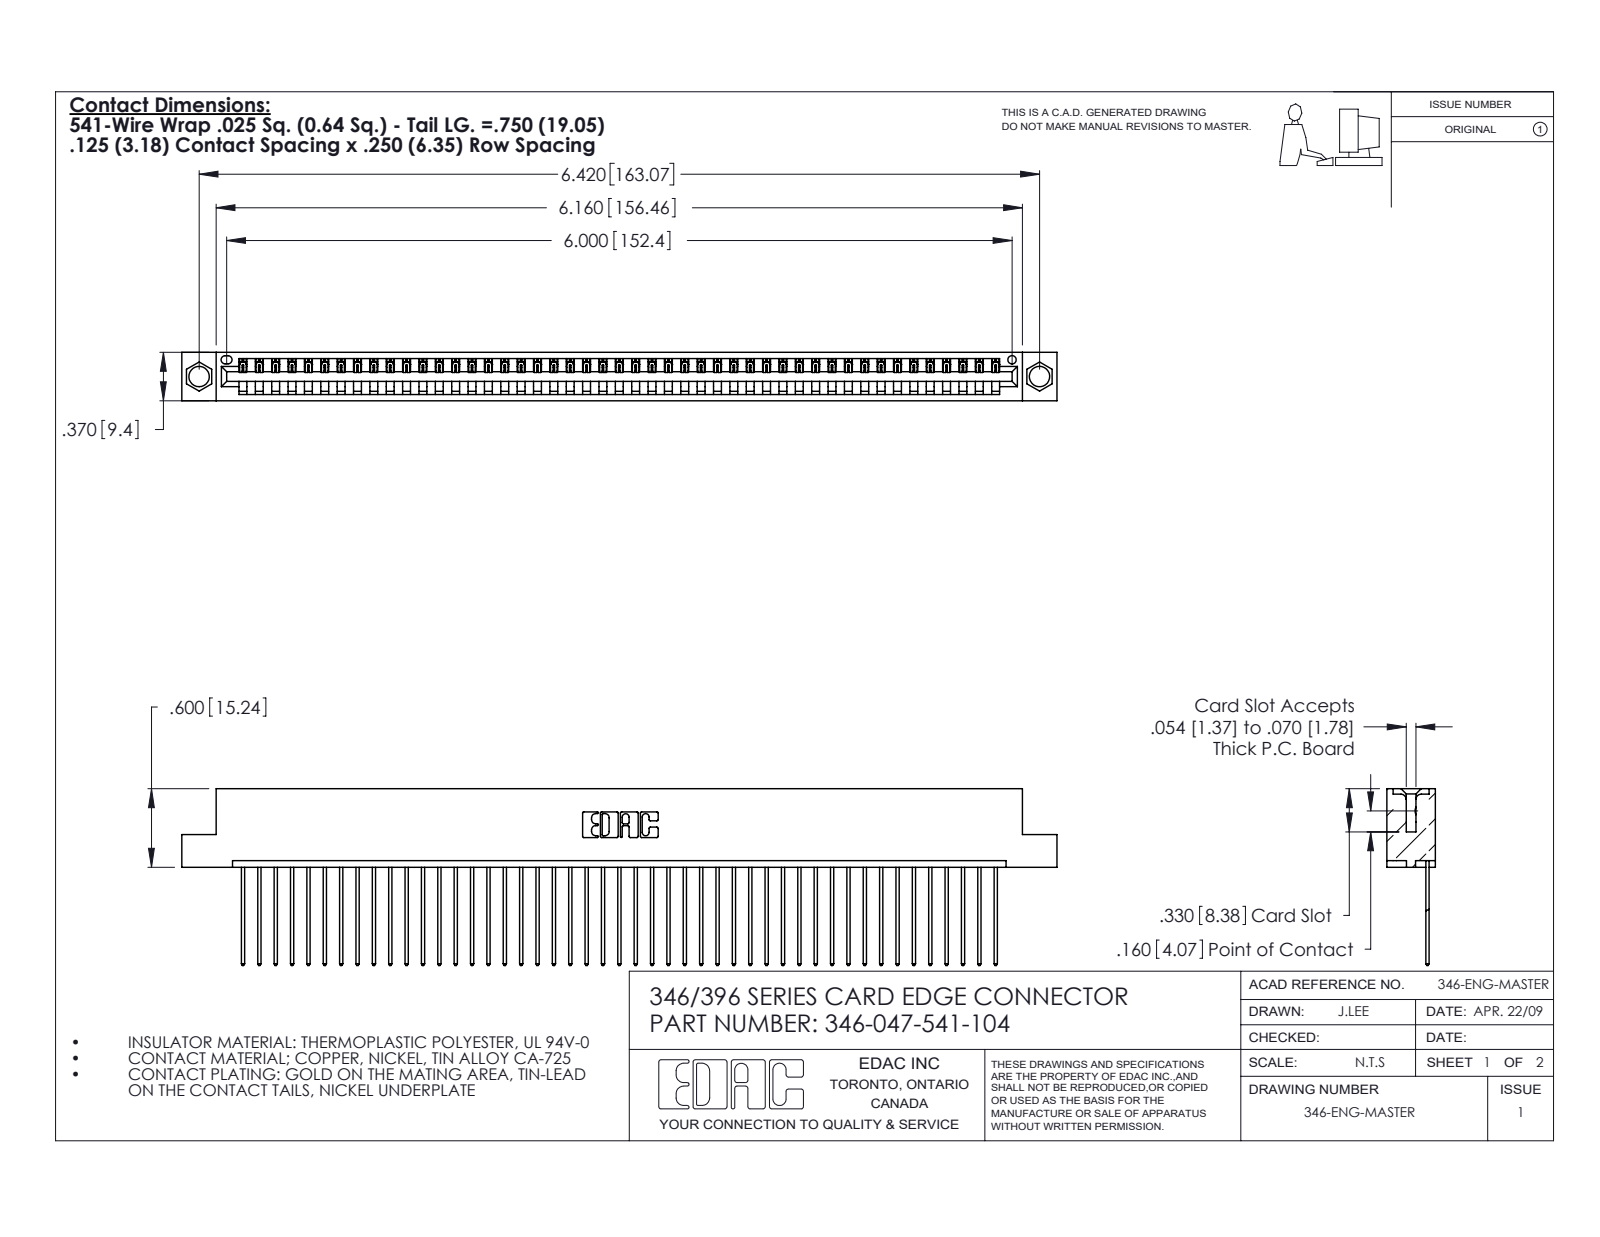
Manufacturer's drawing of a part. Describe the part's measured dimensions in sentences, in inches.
The part is named "346-047-541-104; 346 Part_Flush Mounting Lugs - 0.156 Dia-TH; 345-292-001_345-293-141". Its 3-D file was written by "SolidWorks 2020 (CONFIG_CONTROL_DESIGN)". It is 48 solids with 2862 faces: 1970 planar, 892 cylindrical and 0 other. Overall it measures 6.685 by 1.35 by 0.37 inches. Its volume is 0.997 cubic inches and its surface area 32.92 square inches. Round holes: 2 of diameter 0.156, 1 of diameter 0.064. Partial cylindrical surfaces (rounded edges, fillets, slot ends): 94 of radius 0.006, 94 of radius 0.01, 22 of radius 0.01, 6 of radius 0.007, 6 of radius 0.031, 3 of radius 0.026, 2 of radius 0.031, 2 of radius 0.04. The main face-to-face distances are 0.048, 0.322, 0.37, 0.25, 0.072, 0.298, 0.025, 0.148, 0.222, 0.1. The hole center spacings are 0.246, 6.211, 6.42.
